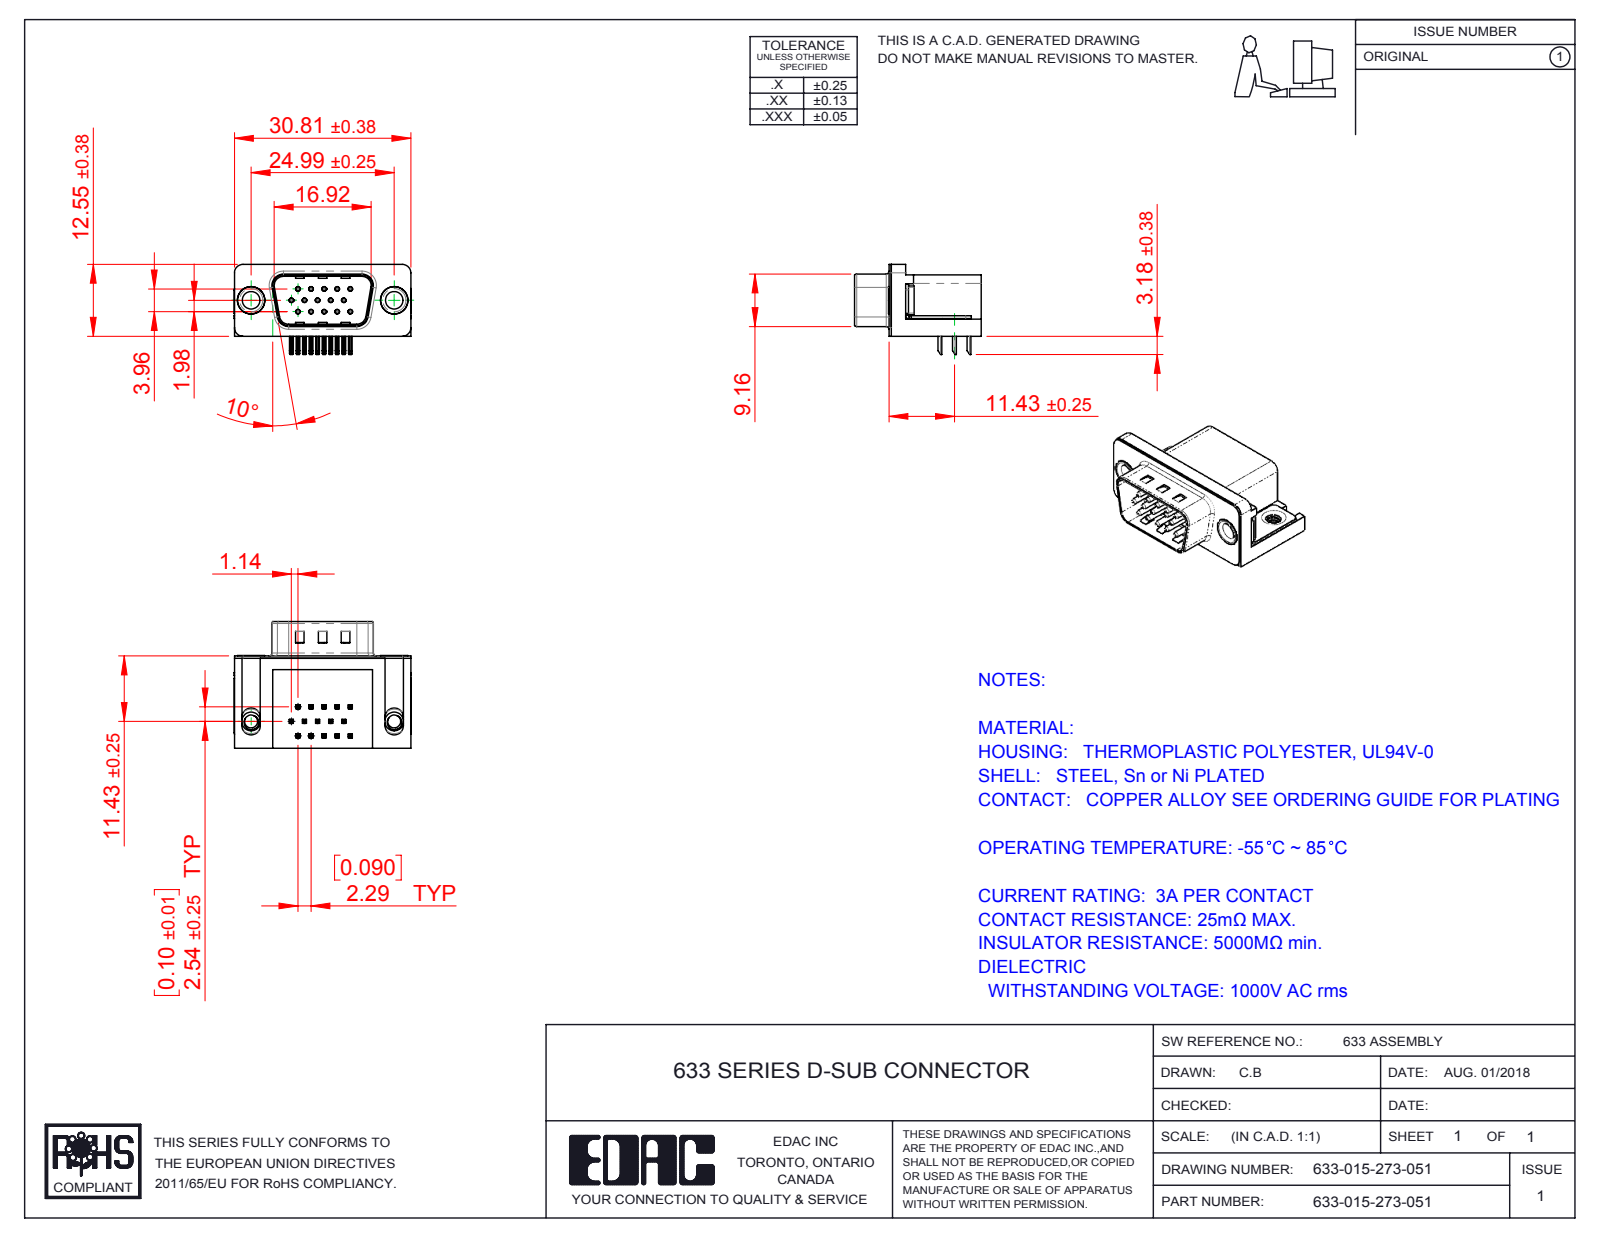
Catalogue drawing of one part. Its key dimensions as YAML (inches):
part_name: "633 Contact Middle_Recessed; 633 4-40 Threaded Board Mount; 633 Contact Top; 633 Housing_15 Contact (+5 more)"
step_written_by: "SolidWorks 2016 (CONFIG_CONTROL_DESIGN)"
units: inches
bodies: {solids: 21, faces: 1433, planar: 861, cylindrical: 437, other: 135}
overall_size: [1.216, 0.87, 0.619]
volume: 0.249
surface_area: 8.497
round_holes:
  - {diameter: 0.014, count: 15}
  - {diameter: 0.031, count: 15}
  - {diameter: 0.089, count: 2}
  - {diameter: 0.12, count: 2}
  - {diameter: 0.157, count: 2}
  - {diameter: 0.189, count: 2}
  - {diameter: 0.197, count: 2}
round_bosses_or_shafts:
  - {diameter: 0.03, count: 15}
  - {diameter: 0.193, count: 2}
  - {diameter: 0.187, count: 2}
  - {diameter: 0.152, count: 2}
  - {diameter: 0.128, count: 2}
partial_cylinders:
  - {radius: 0.01, count: 68}
  - {radius: 0.005, count: 30}
  - {radius: 0.039, count: 16}
  - {radius: 0.02, count: 9}
  - {radius: 0.063, count: 8}
  - {radius: 0.059, count: 7}
  - {radius: 0.035, count: 4}
  - {radius: 0.079, count: 4}
face_to_face_distances: [0.016, 0.407, 0.618, 0.02, 0.114, 0.098, 0.264, 0.634, 0.014, 0.421]
hole_center_spacings: [0.156, 0.09, 0.18, 0.09, 0.238, 0.27, 0.312, 0.238]
